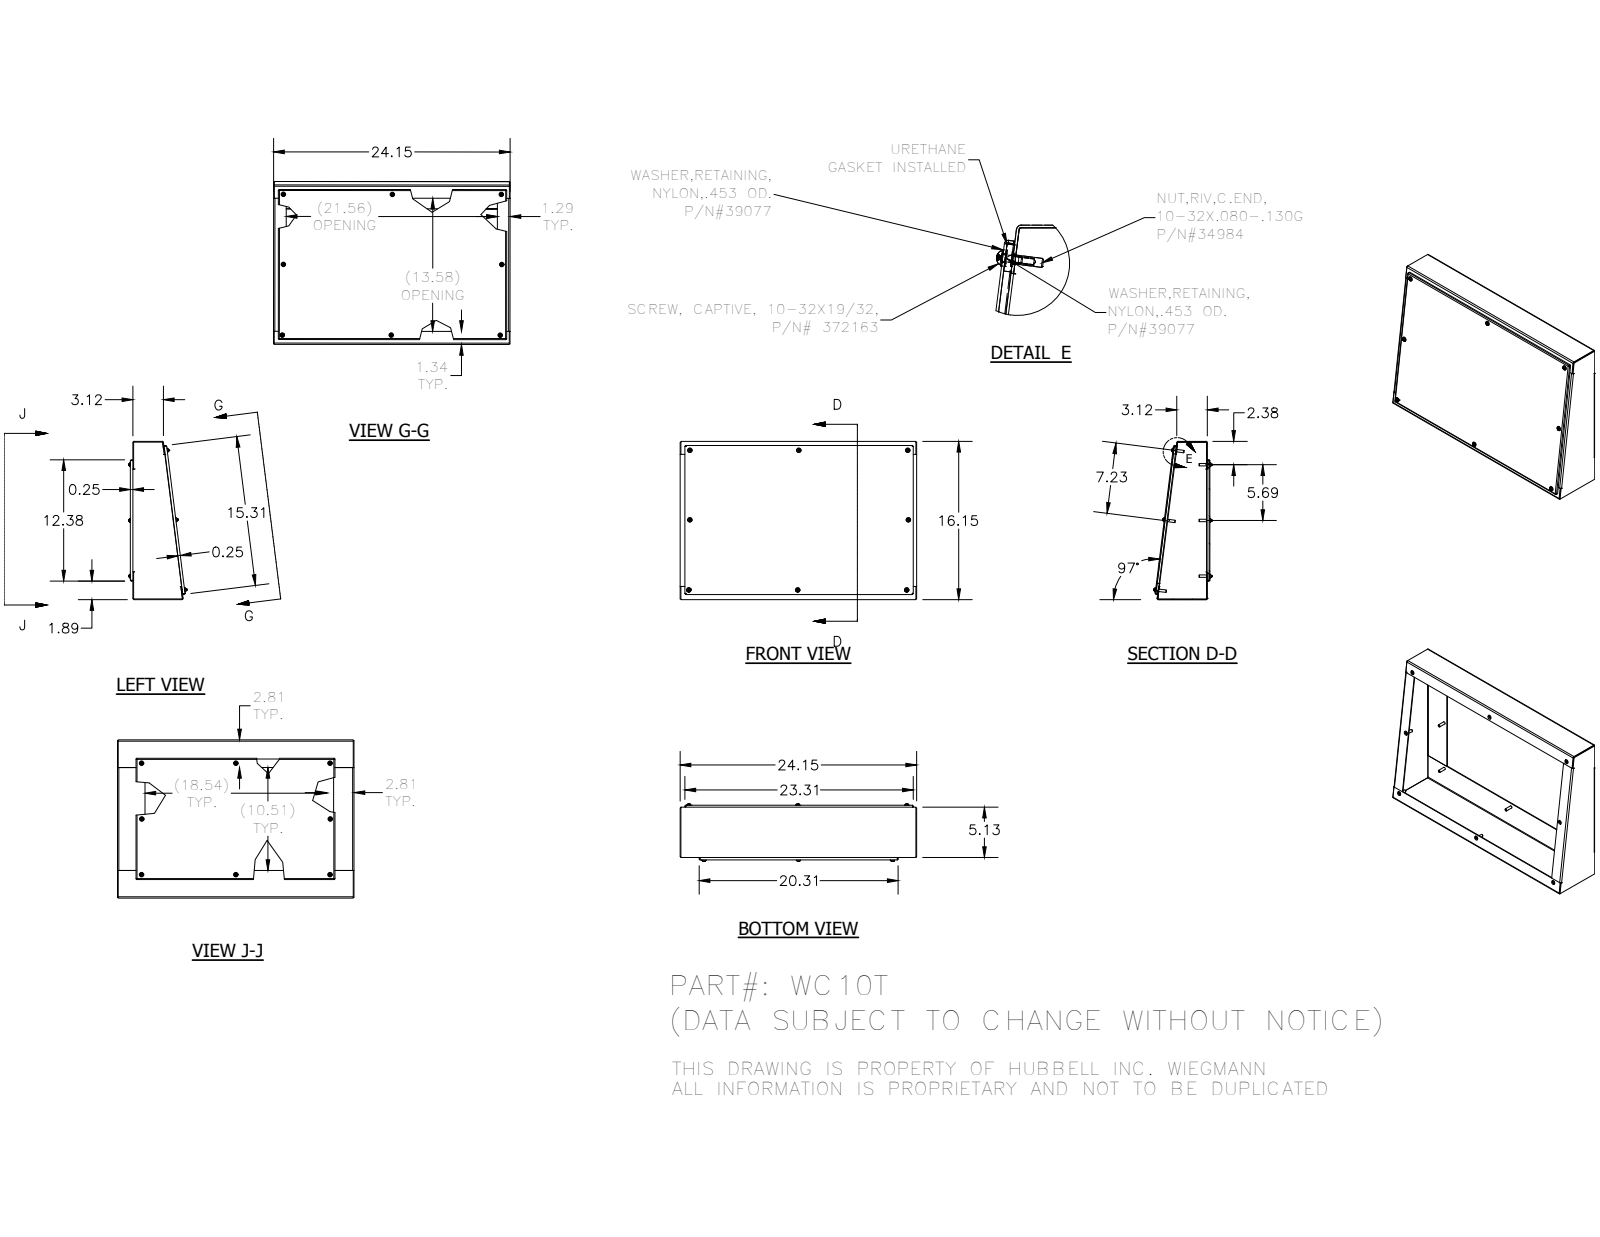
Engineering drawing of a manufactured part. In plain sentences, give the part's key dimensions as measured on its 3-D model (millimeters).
The part is named "WC10TBTM; WC10_TLS; WC10_TRS; WC10TTOP (+8 more)". Its 3-D file was written by "Autodesk Inventor 2016 (AUTOMOTIVE_DESIGN)". It is 72 solids with 1688 faces: 968 planar, 352 cylindrical and 368 other. Overall it measures 613.36 by 410.16 by 149.45 millimeters. Its volume is 1 855 000 cubic millimeters and its surface area 1 804 000 square millimeters. Round holes: 23 of diameter 7.06, 16 of diameter 3.96, 16 of diameter 4.98, 16 of diameter 6.35, 16 of diameter 6.53, 9 of diameter 4.55. Round bosses or shafts: 23 of diameter 11.51, 16 of diameter 10.31, 16 of diameter 9.47, 16 of diameter 6.3, 16 of diameter 4.83. Partial cylindrical surfaces (rounded edges, fillets, slot ends): 14 of radius 2.27, 8 of radius 0.79, 8 of radius 2.67, 8 of radius 3.47, 4 of radius 1.59, 4 of radius 1.59. The main face-to-face distances are 1.88, 6.35, 4.47, 8.23, 408.28, 611.48, 406.4, 410.16, 609.6, 613.36. The hole center spacings are 565.15, 364.9, 282.57, 282.58, 364.91, 363.52, 288.81, 459.87.
